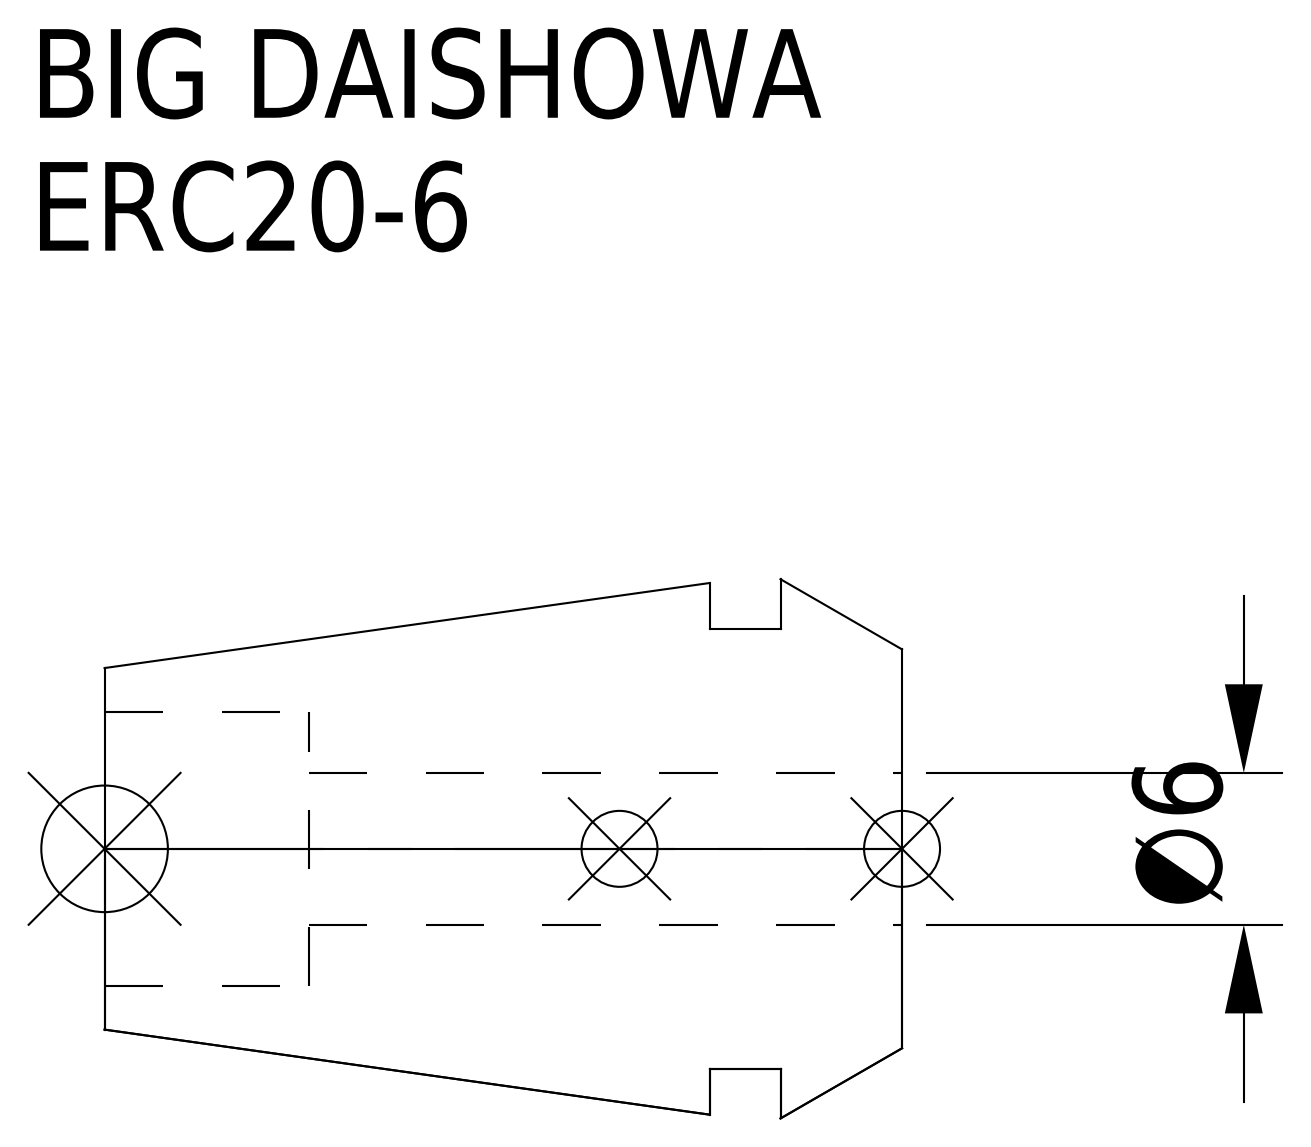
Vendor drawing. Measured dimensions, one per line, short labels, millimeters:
name: ERC20-6
written by: CREO PARAMETRIC BY PTC INC, 2016380 (AUTOMOTIVE_DESIGN)
unit: mm
bodies: 1 solid, 15 faces (5 planar, 6 cylindrical, 4 other)
size: 31.5 × 21.3 × 21.3
volume: 6 481 mm³; area: 3 054 mm²
holes: 1× ⌀6, 1× ⌀10.8
bosses: 1× ⌀17.4
face distances: 4.8, 7.6, 2.8, 31.5, 26.7, 23.9, 23.44, 18.64, 15.84, 8.06
